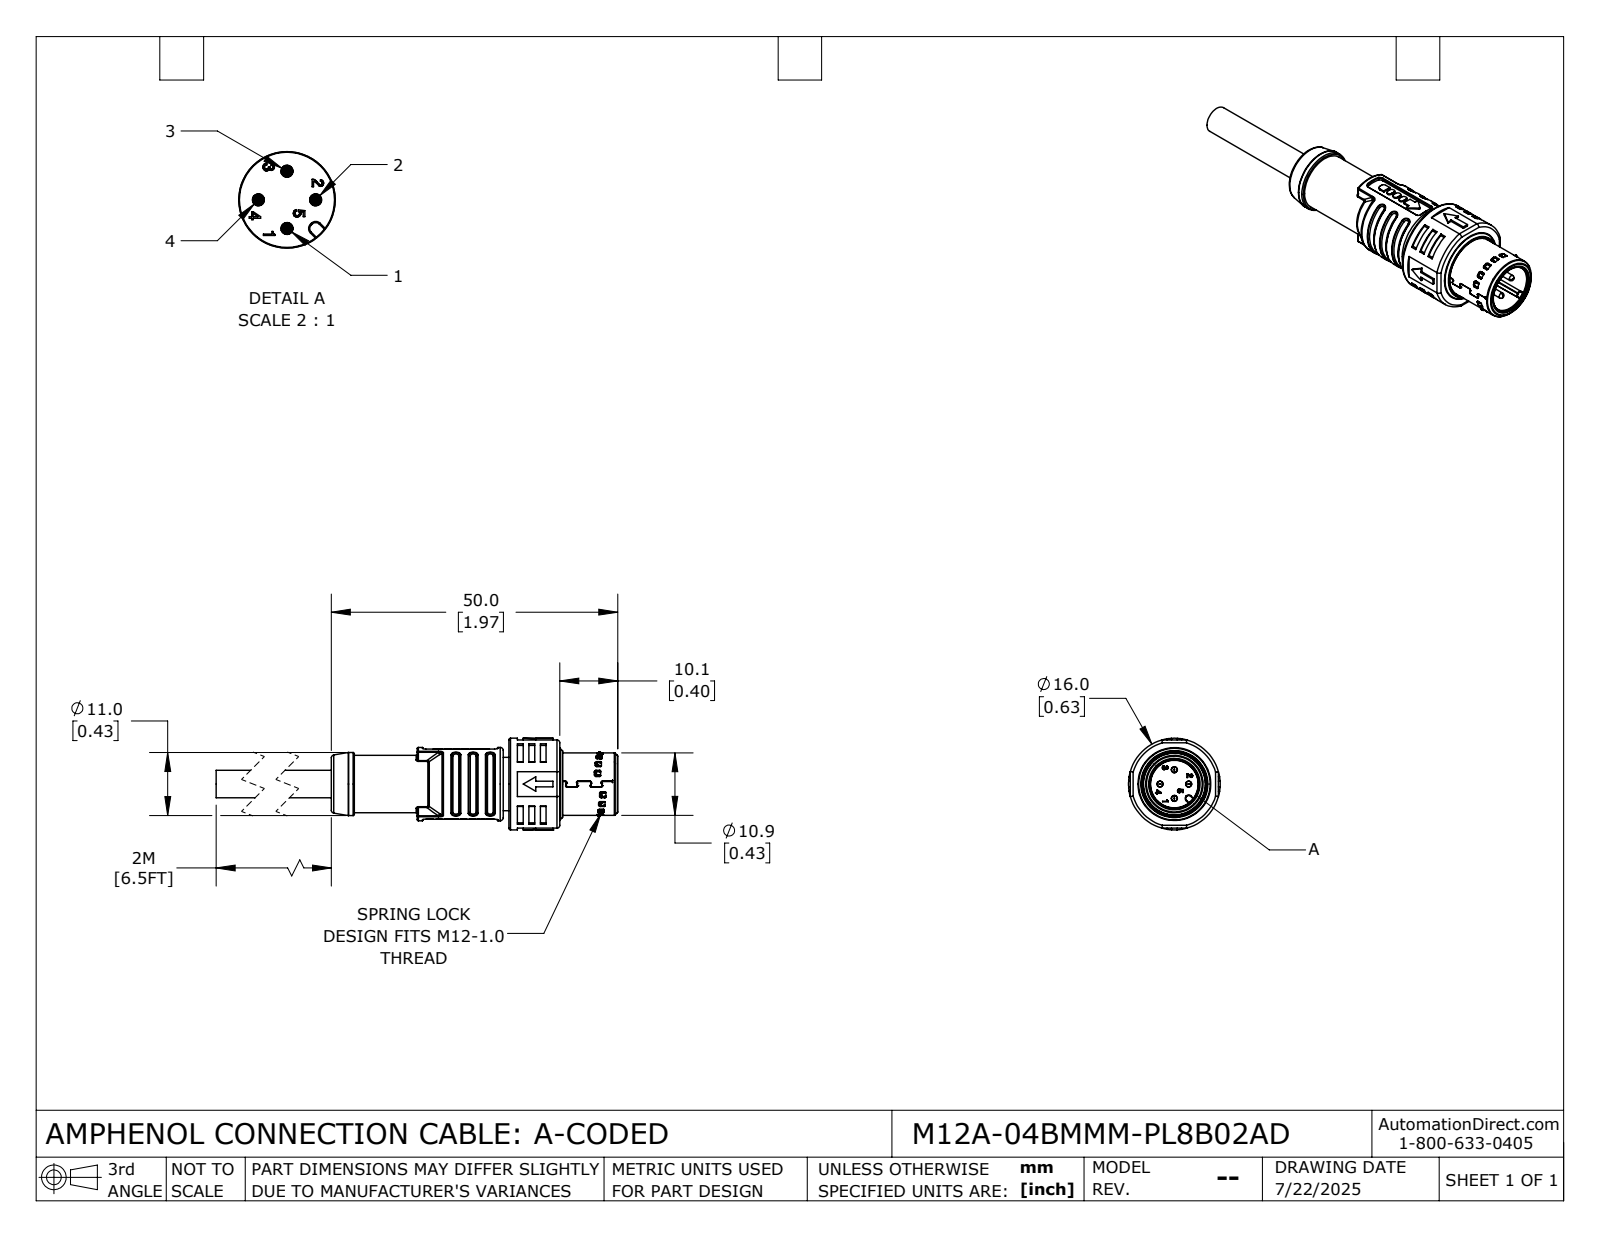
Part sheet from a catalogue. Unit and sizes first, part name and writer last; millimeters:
Units: millimetres
Overall size (bounding box): 72.7 × 16 × 16
Round holes (diameter × count): ⌀1 ×4, ⌀1.4 ×4, ⌀8.3 ×1, ⌀9 ×1, ⌀10.2 ×1, ⌀10.5 ×1, ⌀11.5 ×1, ⌀11.8 ×1, ⌀14.2 ×1
Round bosses / shafts (diameter × count): ⌀1.4 ×4, ⌀1 ×4, ⌀16 ×1, ⌀14.1 ×1, ⌀12.8 ×1, ⌀12.4 ×1, ⌀11 ×1, ⌀10.9 ×1
Partial cylindrical surfaces — rounded edges, fillets, slot ends (radius × count): R0.2 ×114, R0.3 ×66, R0.3 ×64, R0.2 ×44, R0.5 ×38, R0.1 ×12, R0.7 ×11, R0.1 ×10
Main face-to-face distances: 1, 10.1, 8.9, 8.6, 2.5, 1.5, 1.2, 32.5, 15.4, 41.1
Hole centre spacings: 2.5, 3.5, 5
Volume: 5 180 mm³ · Surface area: 5 970 mm²
Bodies: 1 solid, 2276 faces (1081 planar, 672 cylindrical, 523 other)
Part name (STEP PRODUCT): M12A-04BMMM-PL8B02AD
STEP written by: SolidWorks 2024 (CONFIG_CONTROL_DESIGN)
